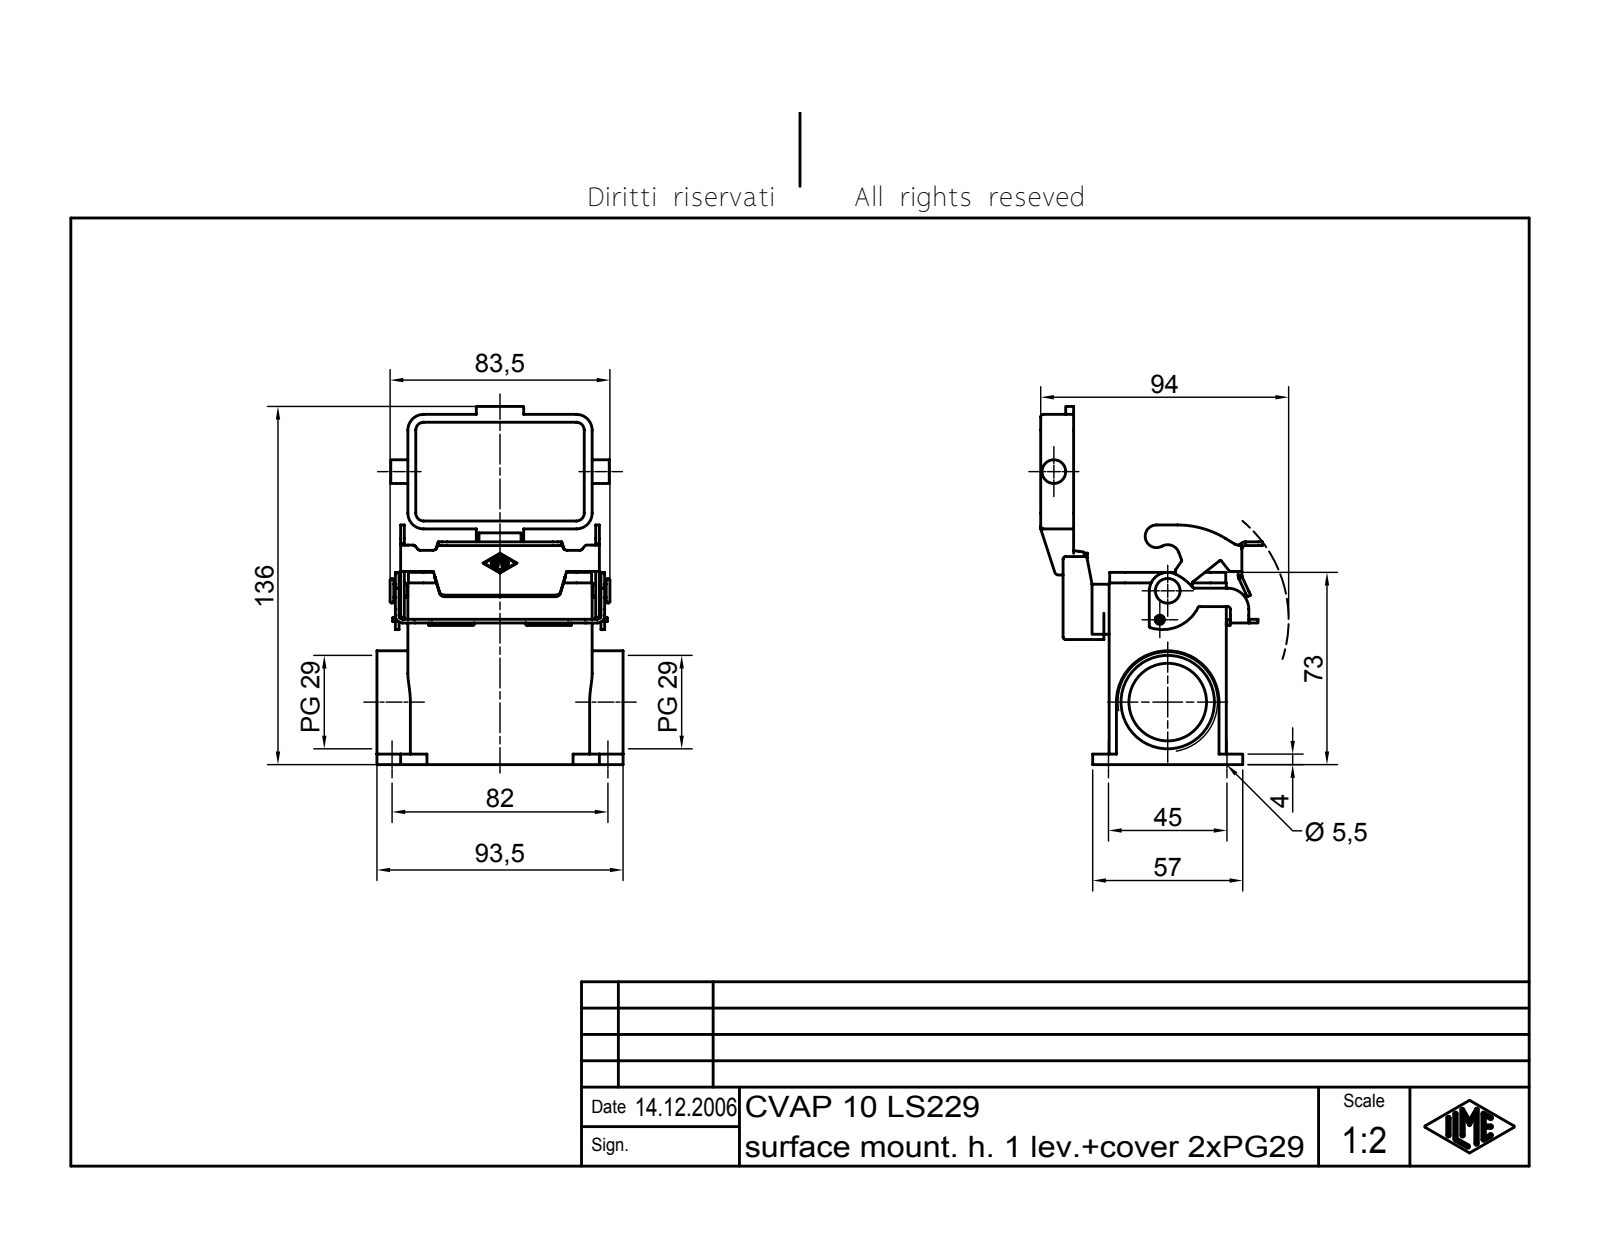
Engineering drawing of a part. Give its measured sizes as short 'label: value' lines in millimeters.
name: CVAP 10 LS229
written by: Autodesk Inventor 7 (AUTOMOTIVE_DESIGN)
unit: mm
bodies: 4 solids, 574 faces (222 planar, 187 cylindrical, 165 other)
size: 136 × 93.5 × 84.23
volume: 121 011 mm³; area: 69 360 mm²
holes: 4× ⌀5.5, 1× ⌀3.5, 1× ⌀4, 1× ⌀29.48, 1× ⌀35.48
bosses: 2× ⌀5, 1× ⌀9, 1× ⌀7, 1× ⌀3.2, 1× ⌀3
rounds: 27× R1, 15× R0.25, 10× R0.5, 10× R1.5, 8× R6, 7× R2, 6× R1.4, 6× R2.8
face distances: 4, 40.5, 44.5, 10, 36.5, 30, 70.5, 66.5, 26, 64
hole spacings: 45, 82, 93.54, 31.4
